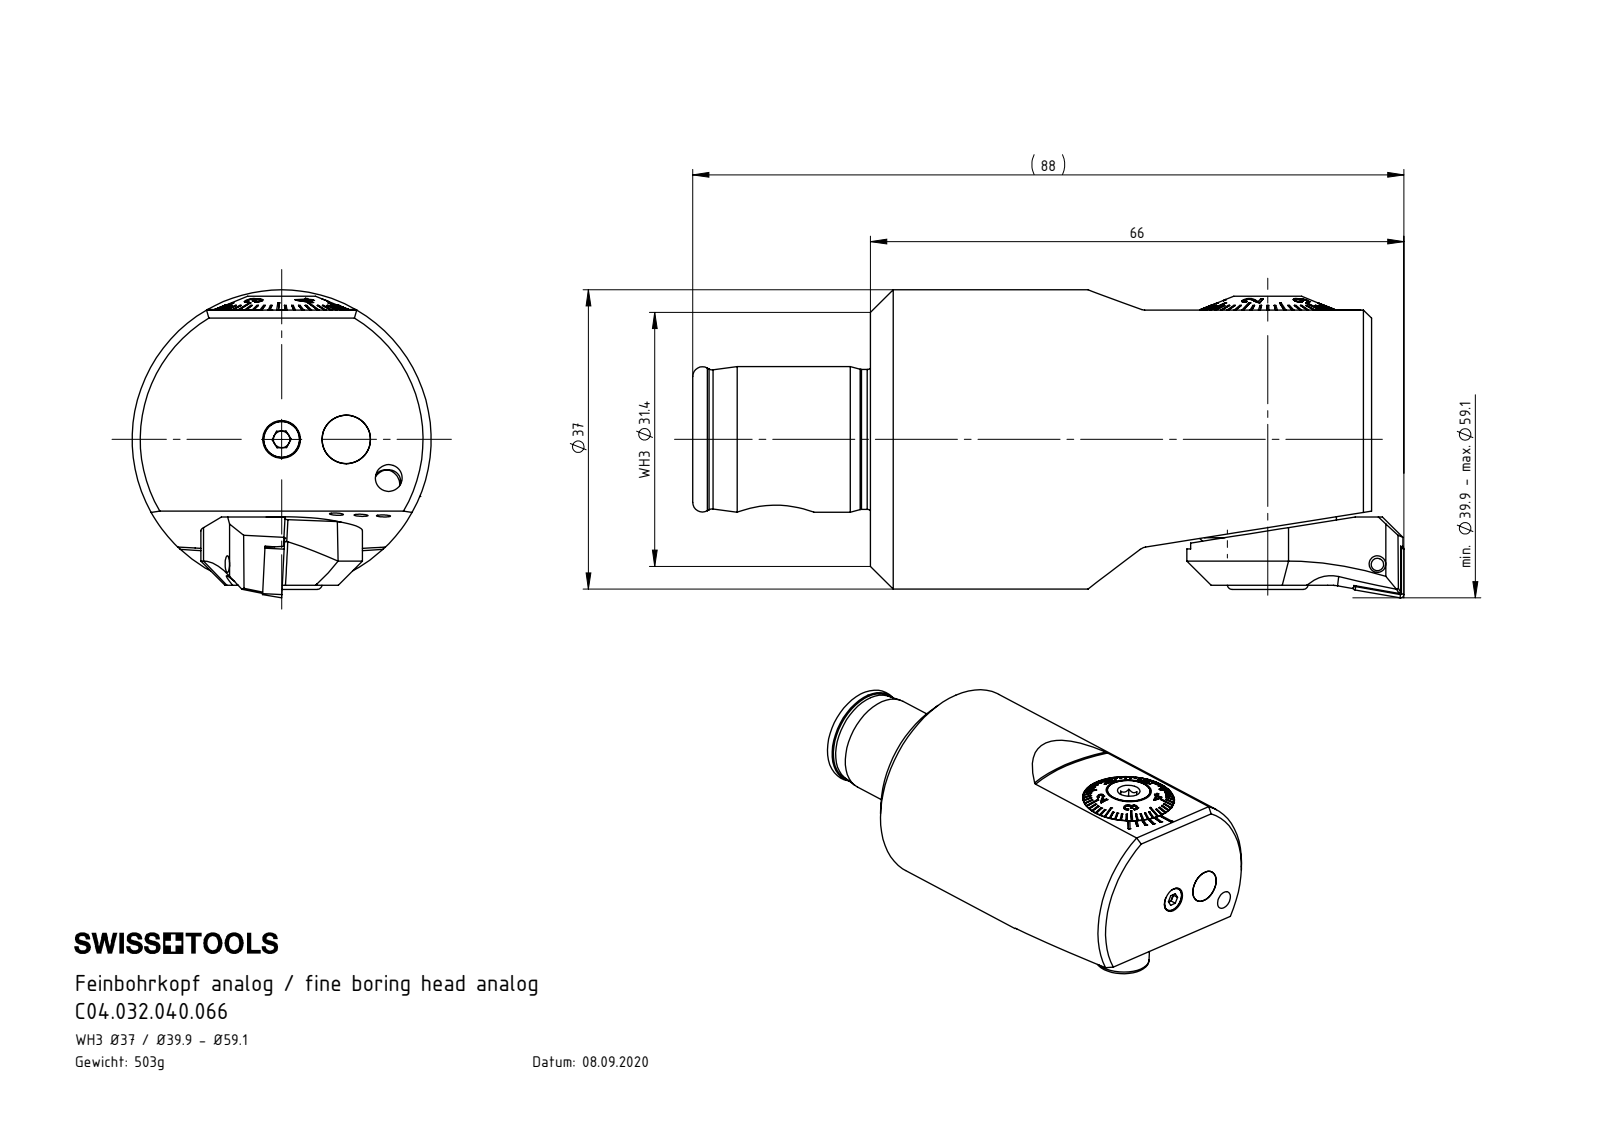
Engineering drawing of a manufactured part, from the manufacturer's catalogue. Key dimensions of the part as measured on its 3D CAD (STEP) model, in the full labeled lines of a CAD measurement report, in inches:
Part name (STEP PRODUCT): ISO 4026 - M6 x 8; F32-BG1.AA4.017_Standart; Klebstoff D6; F32-BG2.017.004_A (+8 more)
STEP written by: SolidWorks 2017 (CONFIG_CONTROL_DESIGN)
Units: inches
Bodies: 13 solids, 666 faces (300 planar, 110 cylindrical, 256 other)
Overall size (bounding box): 3.307 × 1.459 × 1.457
Volume: 3.855 in³ · Surface area: 30.6 in²
Round holes (diameter × count): ⌀0.059 ×3, ⌀0.13 ×2, ⌀0.197 ×2, ⌀0.081 ×1, ⌀0.106 ×1, ⌀0.114 ×1, ⌀0.118 ×1, ⌀0.165 ×1, ⌀0.236 ×1, ⌀0.268 ×1, ⌀0.276 ×1, ⌀0.291 ×1
Round bosses / shafts (diameter × count): ⌀0.236 ×2, ⌀1.457 ×1, ⌀0.709 ×1, ⌀0.681 ×1, ⌀0.669 ×1, ⌀0.669 ×1, ⌀0.663 ×1, ⌀0.577 ×1
Partial cylindrical surfaces — rounded edges, fillets, slot ends (radius × count): R0.055 ×4, R0.02 ×3, R0.069 ×2, R0.079 ×2, R0.126 ×1
Main face-to-face distances: 2.441, 0.177, 0.031, 0.146, 0.059, 0.947, 0.087, 0.091, 1.124, 0.866
Hole centre spacings: 0.315, 0.343
